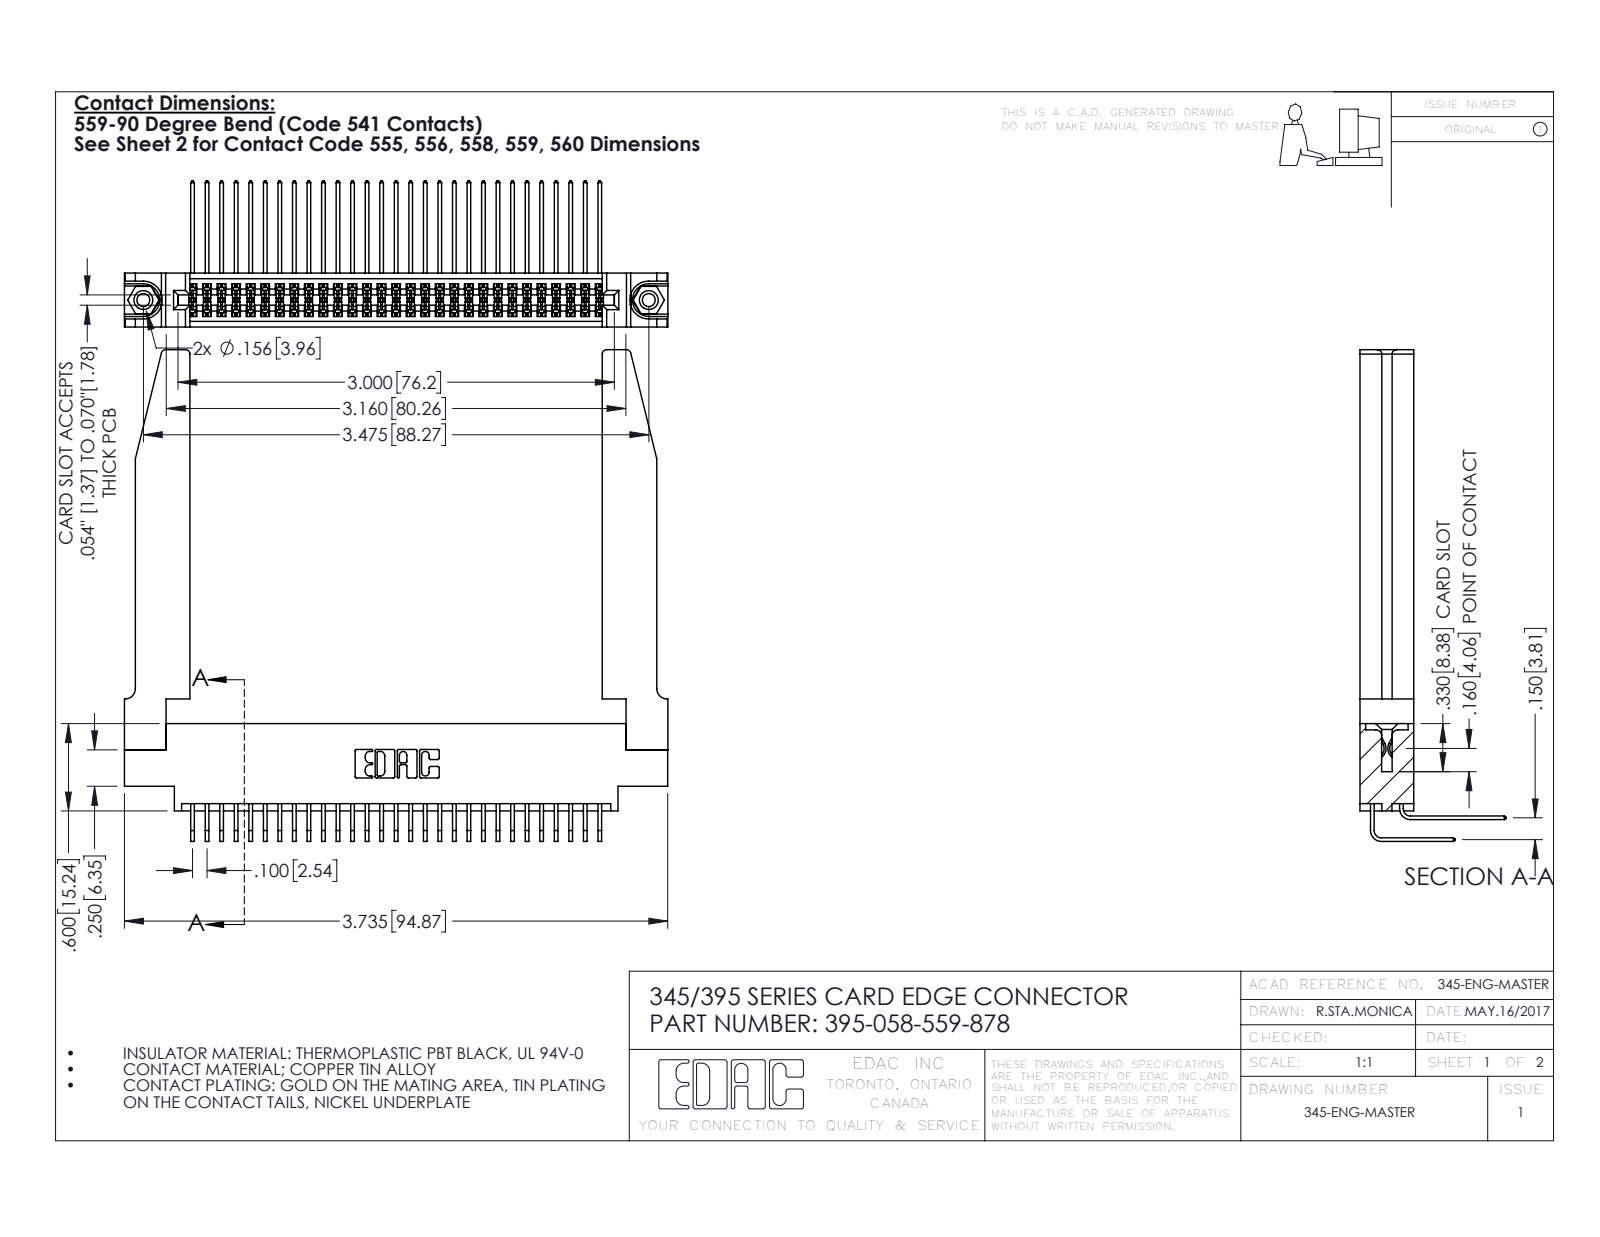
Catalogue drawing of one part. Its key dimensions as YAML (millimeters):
part_name: "345-250-001_345-250-001-102; 395-058-559-878; 345 Part_0.170 Offset - 0.156 Dia-TH; 345-220-078_345-220-078 (+2 more)"
step_written_by: "SolidWorks 2016 (CONFIG_CONTROL_DESIGN)"
units: millimeters
bodies: {solids: 63, faces: 3380, planar: 2256, cylindrical: 1072, other: 52}
overall_size: [94.9, 85.8, 25.5]
volume: 17090
surface_area: 22080
round_holes:
  - {diameter: 2.3, count: 2}
  - {diameter: 3.2, count: 2}
  - {diameter: 4, count: 2}
  - {diameter: 1.6, count: 1}
round_bosses_or_shafts:
  - {diameter: 3.9, count: 2}
partial_cylinders:
  - {radius: 0.2, count: 88}
  - {radius: 0.3, count: 22}
  - {radius: 0.8, count: 8}
  - {radius: 0.2, count: 6}
  - {radius: 0.8, count: 6}
  - {radius: 0.7, count: 3}
  - {radius: 0.4, count: 2}
  - {radius: 0.5, count: 2}
face_to_face_distances: [9.4, 1.8, 7.6, 2.5, 6.9, 0.6, 5.1, 5.7, 3.8, 4.4]
hole_center_spacings: [6.9, 82.3, 88.3]
